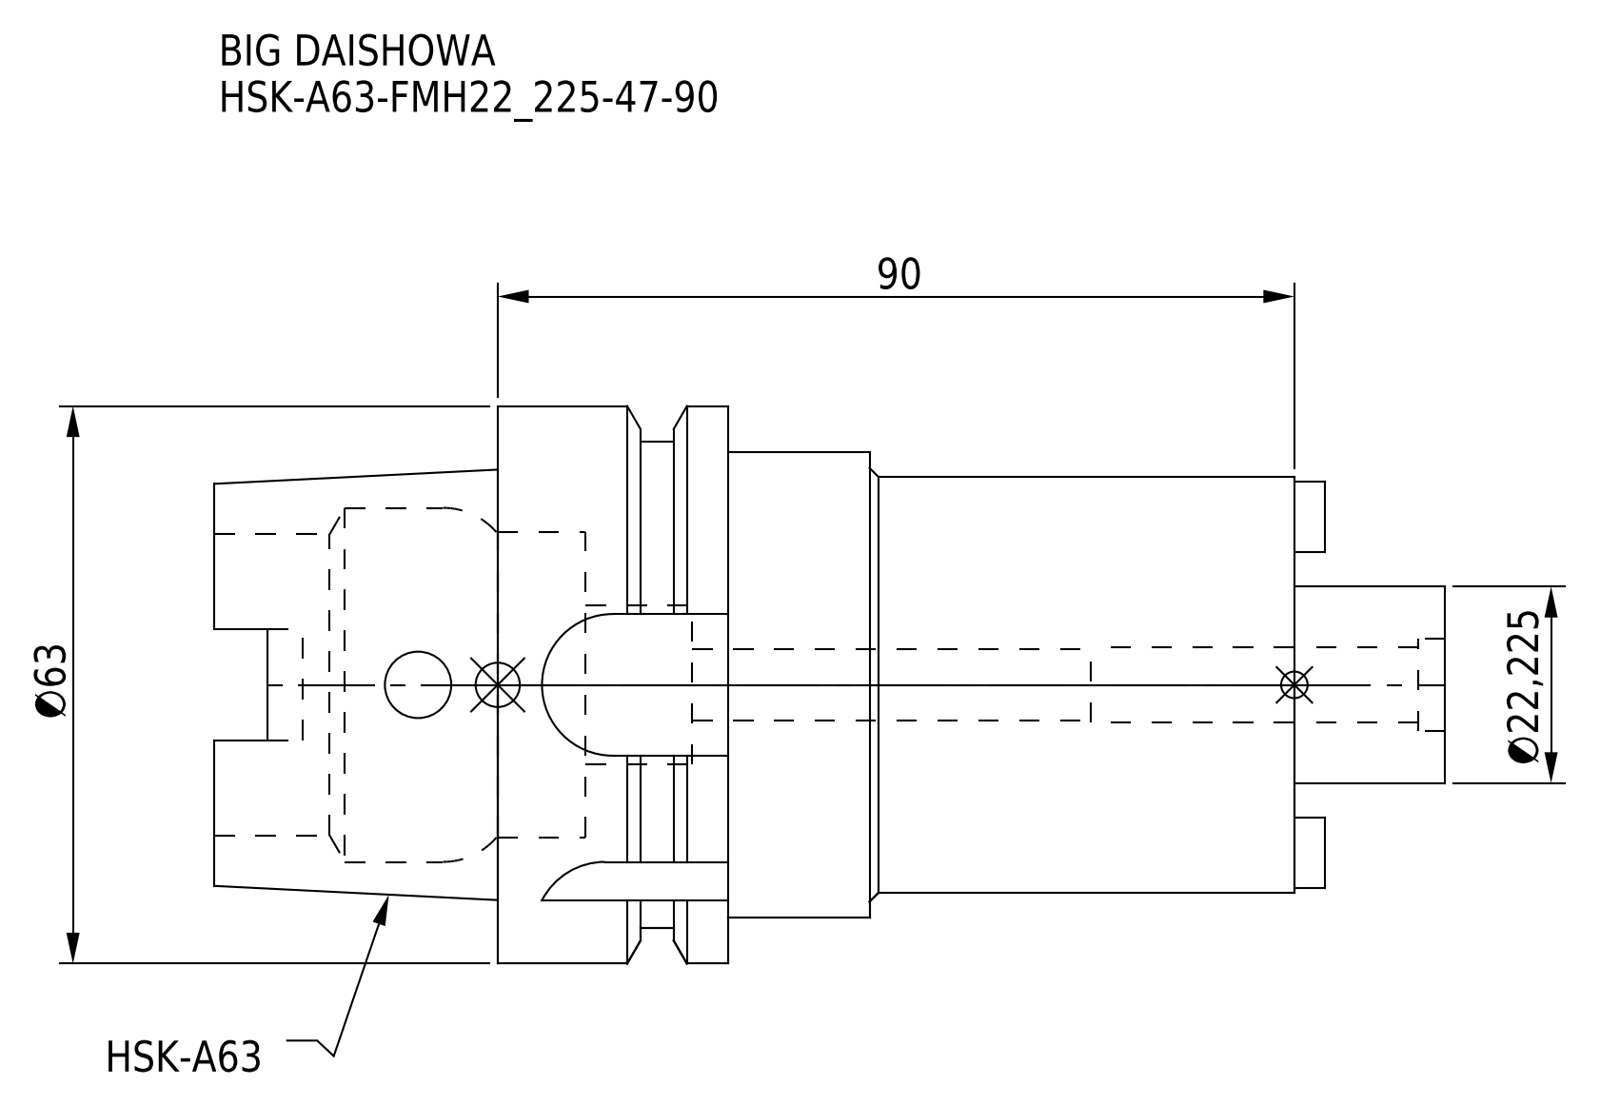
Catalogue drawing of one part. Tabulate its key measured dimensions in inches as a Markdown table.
| quantity | value |
| --- | --- |
| part name | HSK-A63-FMH22_225-47-90 |
| STEP written by | CREO PARAMETRIC BY PTC INC, 2016380 (AUTOMOTIVE_DESIGN) |
| units | inches |
| bodies | 1 solid, 97 faces (45 planar, 38 cylindrical, 14 other) |
| overall size | 5.472 × 2.48 × 2.48 |
| volume | 12.36 in³ |
| surface area | 55.21 in² |
| round holes (diameter × count) | 0.295 × 1, 0.315 × 1, 0.335 × 1, 0.413 × 1, 0.709 × 1, 1.339 × 1, 1.358 × 1, 1.575 × 1 |
| round bosses / shafts (diameter × count) | 2.48 × 1, 2.165 × 1, 2.071 × 1, 1.85 × 1, 0.875 × 1 |
| partial cylindrical surfaces (radius × count) | 0.315 × 2, 0.354 × 1 |
| main face-to-face distances | 3.543, 2.52, 1.024, 3.152, 0.632, 0.392, 1.26, 4.803, 2.283, 1.652 |
